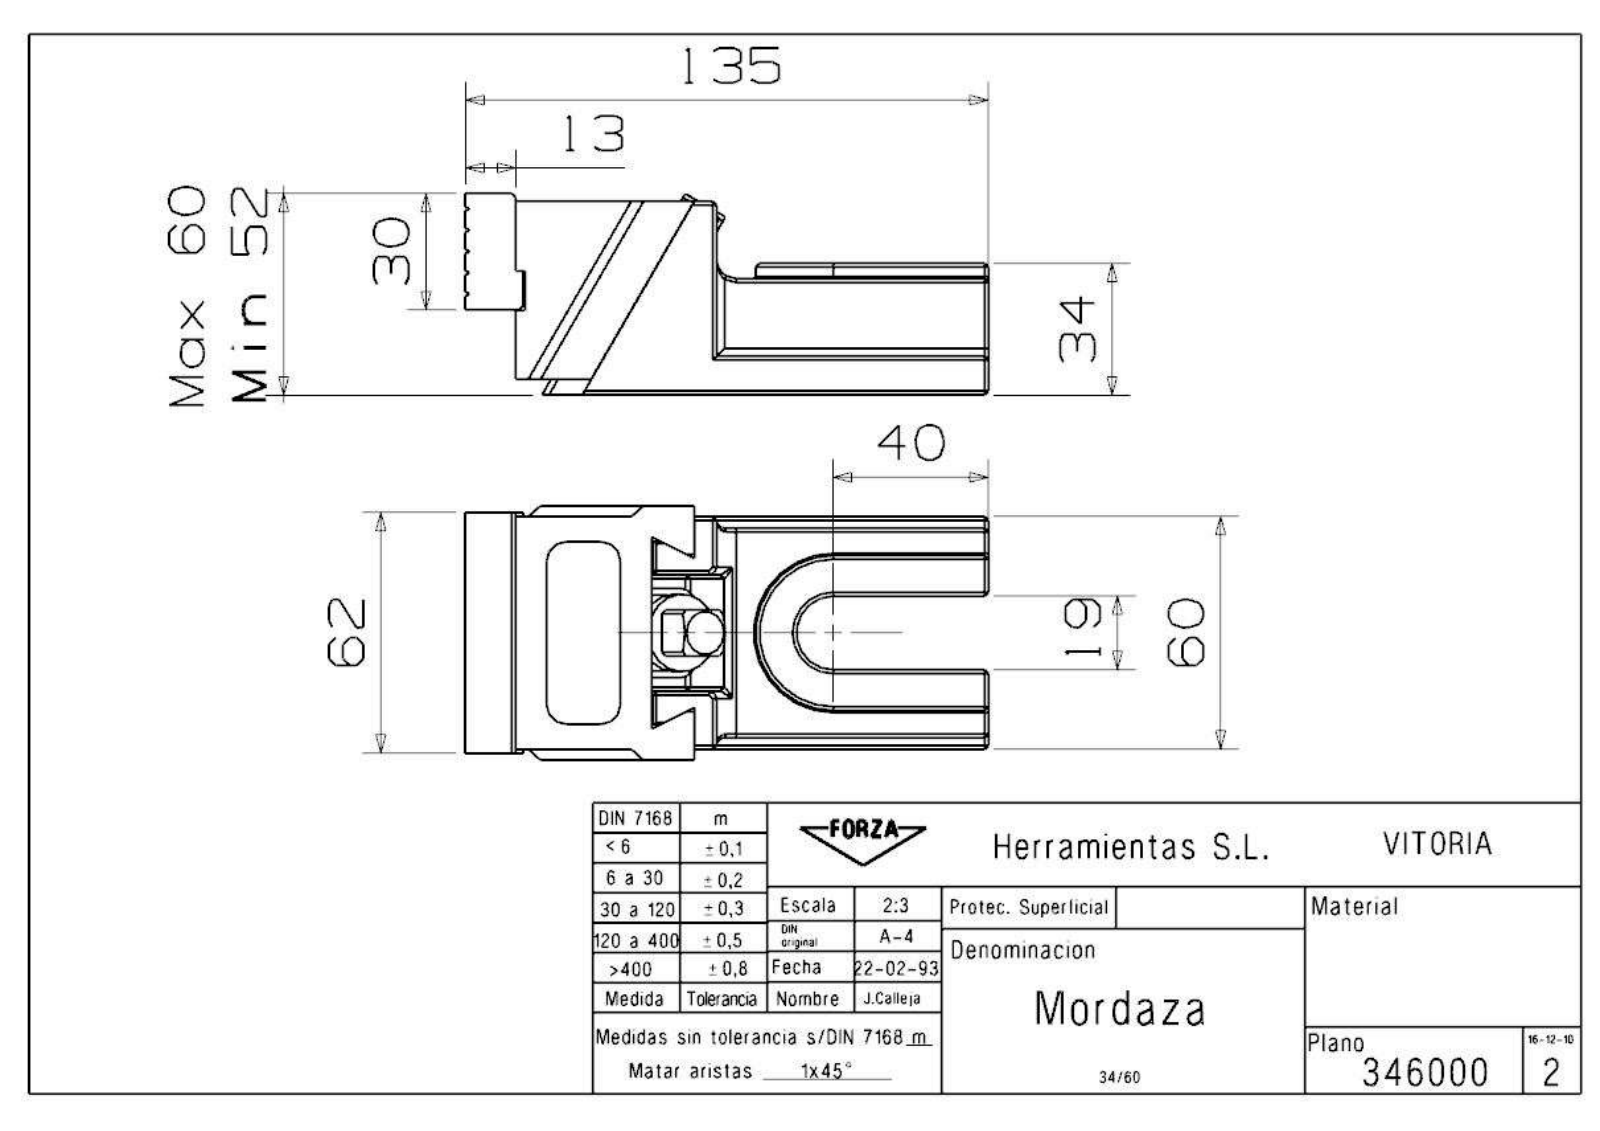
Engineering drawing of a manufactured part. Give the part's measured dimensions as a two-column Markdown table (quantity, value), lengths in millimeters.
| quantity | value |
| --- | --- |
| part name | 346000_Mordaza |
| STEP written by | SIEMENS PLM Software NX 9.0 (CONFIG_CONTROL_DESIGN) |
| units | millimeters |
| bodies | 8 solids, 336 faces (155 planar, 117 cylindrical, 64 other) |
| overall size | 134.83 × 65.5 × 52 |
| volume | 248 053 mm³ |
| surface area | 60 040 mm² |
| round holes (diameter × count) | 2 × 2, 6.99 × 2, 8.5 × 2, 14 × 2, 11 × 1, 11.5 × 1, 14.5 × 1, 15.3 × 1 |
| round bosses / shafts (diameter × count) | 12 × 3, 7.79 × 2, 20 × 1, 18.34 × 1, 15 × 1, 14.3 × 1, 14 × 1, 10.98 × 1 |
| partial cylindrical surfaces (radius × count) | 1 × 46, 0.5 × 11, 2 × 7, 3.5 × 5, 5 × 5, 0.75 × 2, 7.75 × 1, 9.5 × 1 |
| main face-to-face distances | 4, 30, 12, 3, 15, 19, 46, 20.5, 39.5, 17.5 |
| hole center spacings | 9, 9.26, 5.09, 40 |
